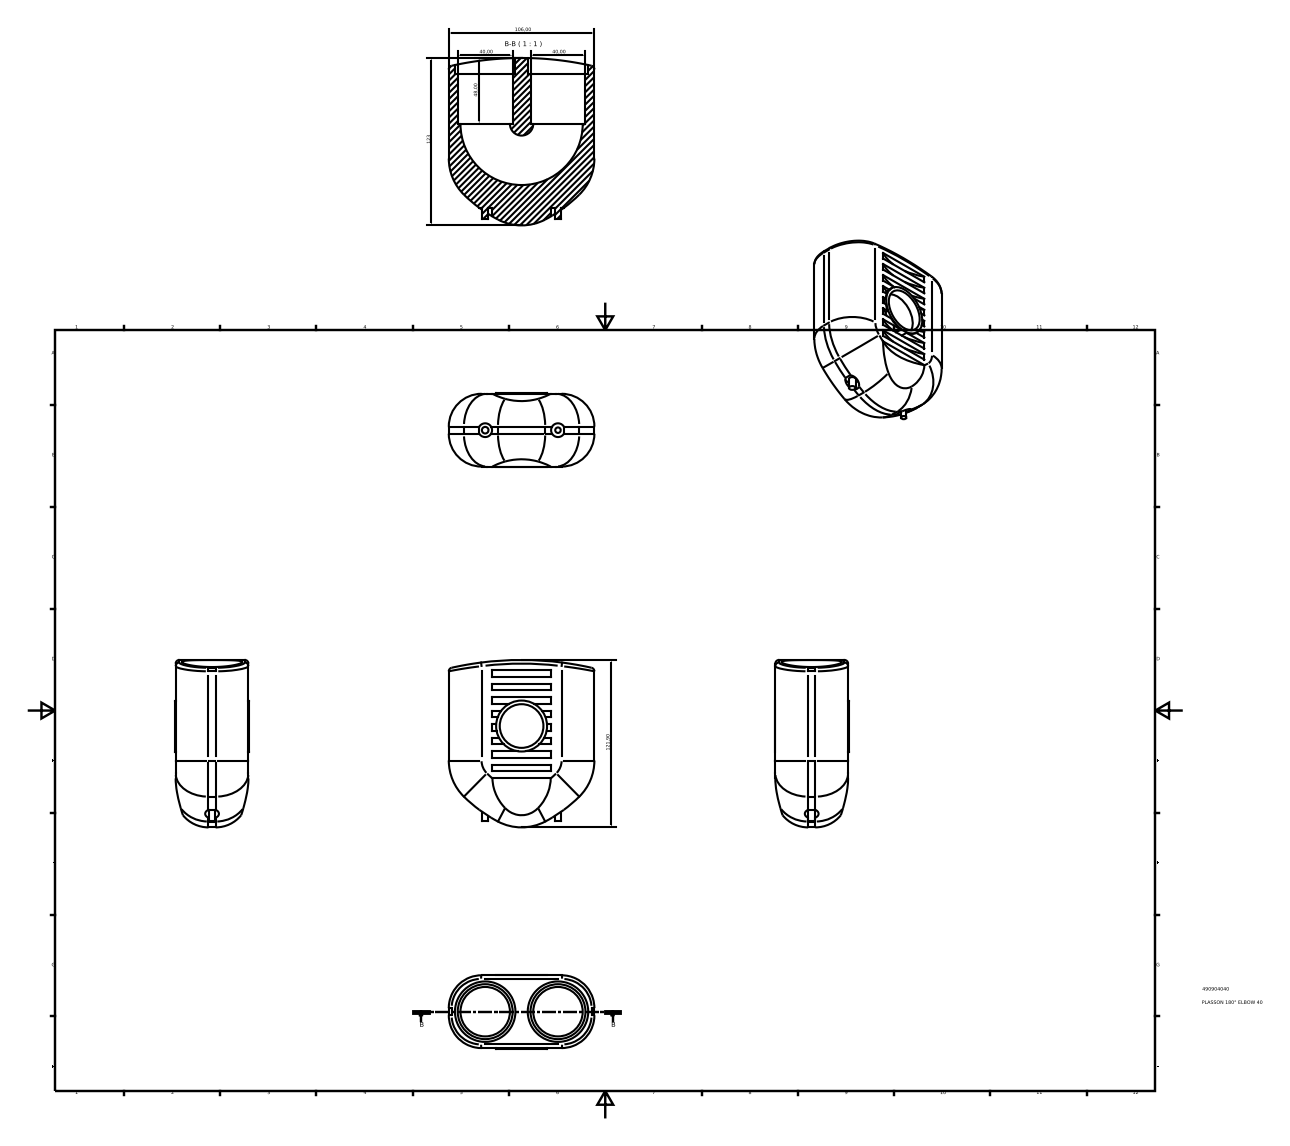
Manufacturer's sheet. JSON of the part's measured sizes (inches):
{"part_name": "490904040", "step_written_by": "Autodesk Inventor 2015 (AUTOMOTIVE_DESIGN)", "units": "inches", "bodies": {"solids": 1, "faces": 133, "planar": 66, "cylindrical": 50, "other": 17}, "overall_size": [4.799, 4.173, 2.128], "volume_in3": 18.63, "surface_area_in2": 95.63, "round_holes": [[0.394, 2], [1.575, 2], [1.732, 2], [1.252, 1]], "round_bosses_or_shafts": [[1.461, 1], [0.189, 1], [0.157, 1]], "partial_cylinders_radius": [[0.939, 4], [1.453, 3], [0.104, 2], [1.774, 2], [4.14, 2], [9.112, 1]], "face_to_face_distances": [0.194, 2.087, 0.387, 0.261, 1.826, 2.324, 0.581, 2.131, 2.518, 1.937], "hole_center_spacings": [2.087]}
